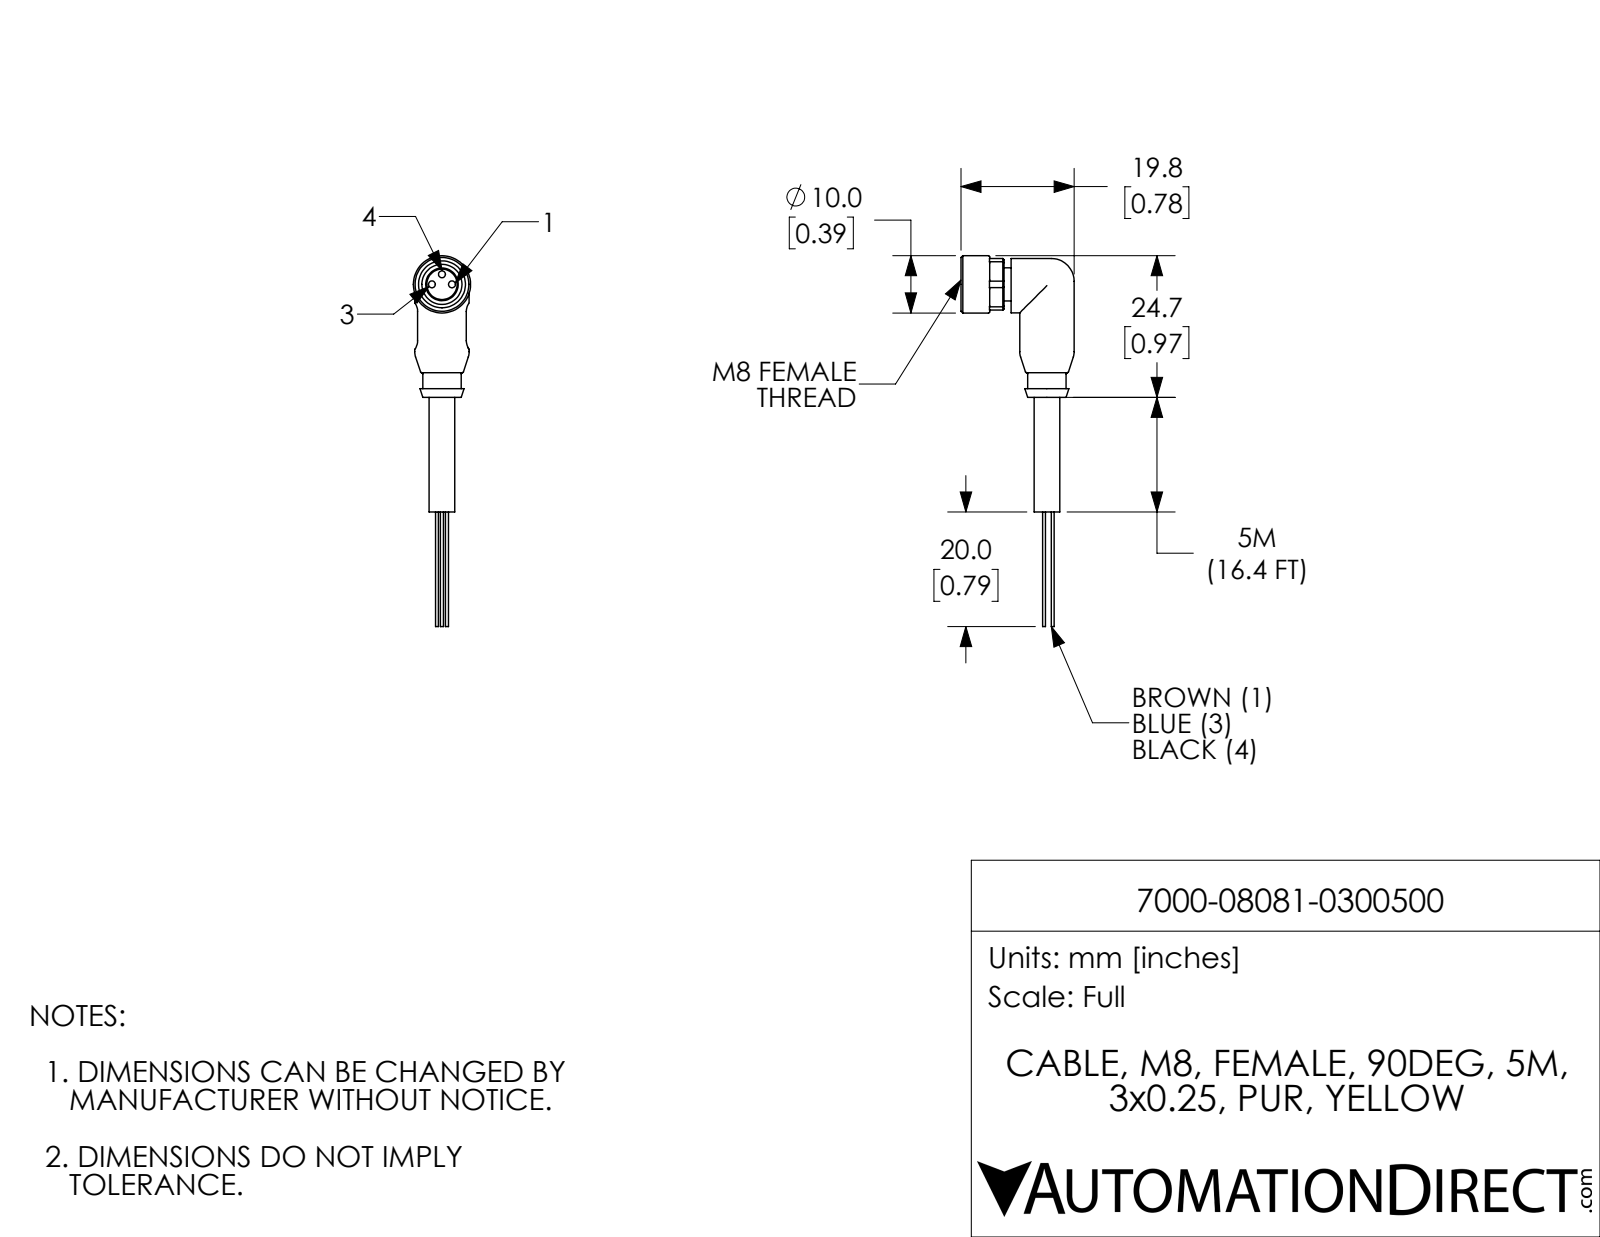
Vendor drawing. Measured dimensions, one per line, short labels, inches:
name: 7000-08081-0300500
written by: SolidWorks 2021 (CONFIG_CONTROL_DESIGN)
unit: in
bodies: 1 solid, 107 faces (35 planar, 43 cylindrical, 29 other)
size: 2.548 × 0.778 × 0.394
volume: 0.147 in³; area: 2.844 in²
holes: 3× ⌀0.047, 1× ⌀0.276
bosses: 3× ⌀0.02, 2× ⌀0.374, 1× ⌀0.394, 1× ⌀0.264, 1× ⌀0.228, 1× ⌀0.224, 1× ⌀0.177
rounds: 4× R0.008, 4× R0.098, 1× R0.193
face distances: 0.049, 0.354, 0.059, 0.335, 0.028, 0.268, 0.317, 0.295, 0.344, 0.787
hole spacings: 0.069, 0.097, 0.138
